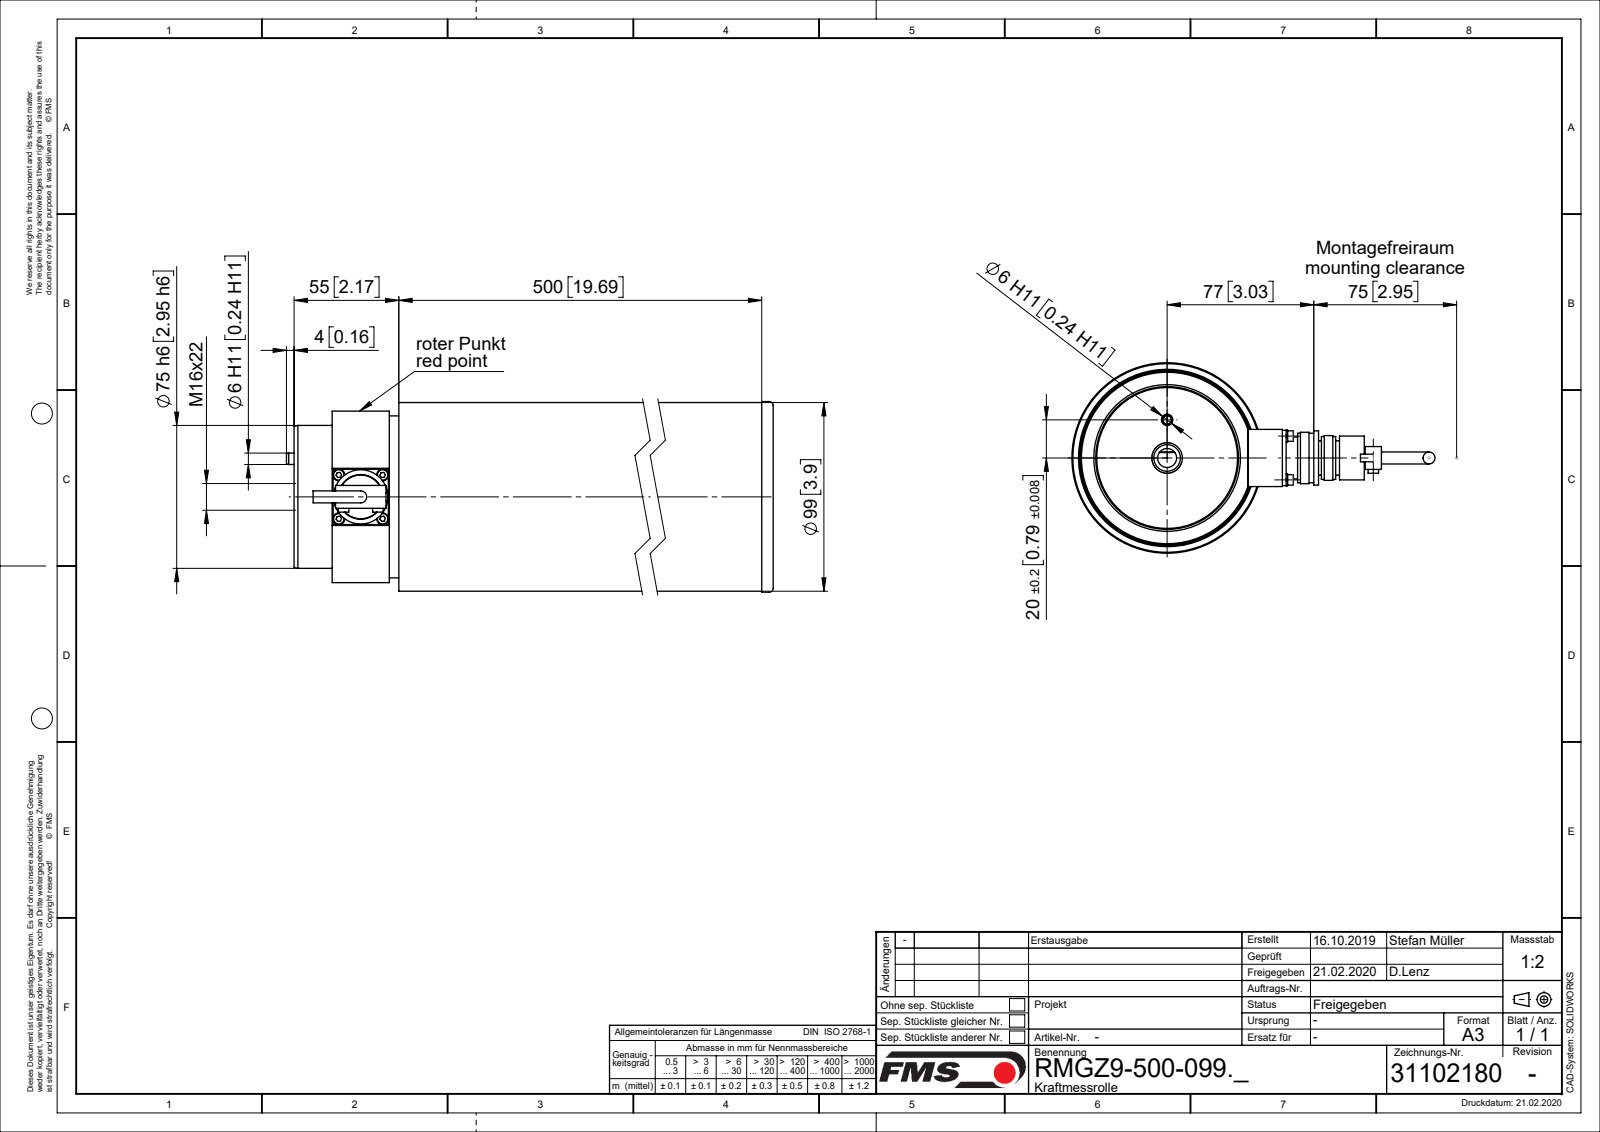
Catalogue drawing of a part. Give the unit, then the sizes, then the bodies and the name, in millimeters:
Units: millimetres
Overall size (bounding box): 565 × 190.65 × 100
Round holes (diameter × count): ⌀2.5 ×4, ⌀3.1 ×4, ⌀3.4 ×4, ⌀3.3 ×1, ⌀5 ×1, ⌀6 ×1, ⌀10 ×1, ⌀12 ×1, ⌀14 ×1, ⌀22 ×1, ⌀23 ×1, ⌀26 ×1
Round bosses / shafts (diameter × count): ⌀5.5 ×6, ⌀6.2 ×4, ⌀3 ×4, ⌀2.5 ×4, ⌀100 ×1, ⌀99 ×1, ⌀91 ×1, ⌀90 ×1
Partial cylindrical surfaces — rounded edges, fillets, slot ends (radius × count): R11 ×4, R4.25 ×2, R17.5 ×1
Main face-to-face distances: 50, 156, 32, 188, 10, 2, 160, 35, 316, 349
Hole centre spacings: 16.26, 23, 32.53, 20
Volume: 1 736 000 mm³ · Surface area: 532 973 mm²
Bodies: 31 solids, 570 faces (162 planar, 234 cylindrical, 174 other)
Part name (STEP PRODUCT): 31102180_stp; 130507.5_01; FLANSCHDOSE_14S-2P_4-POLIG; RKL_6006_01 (+8 more)
STEP written by: SolidWorks 2018 (CONFIG_CONTROL_DESIGN)
